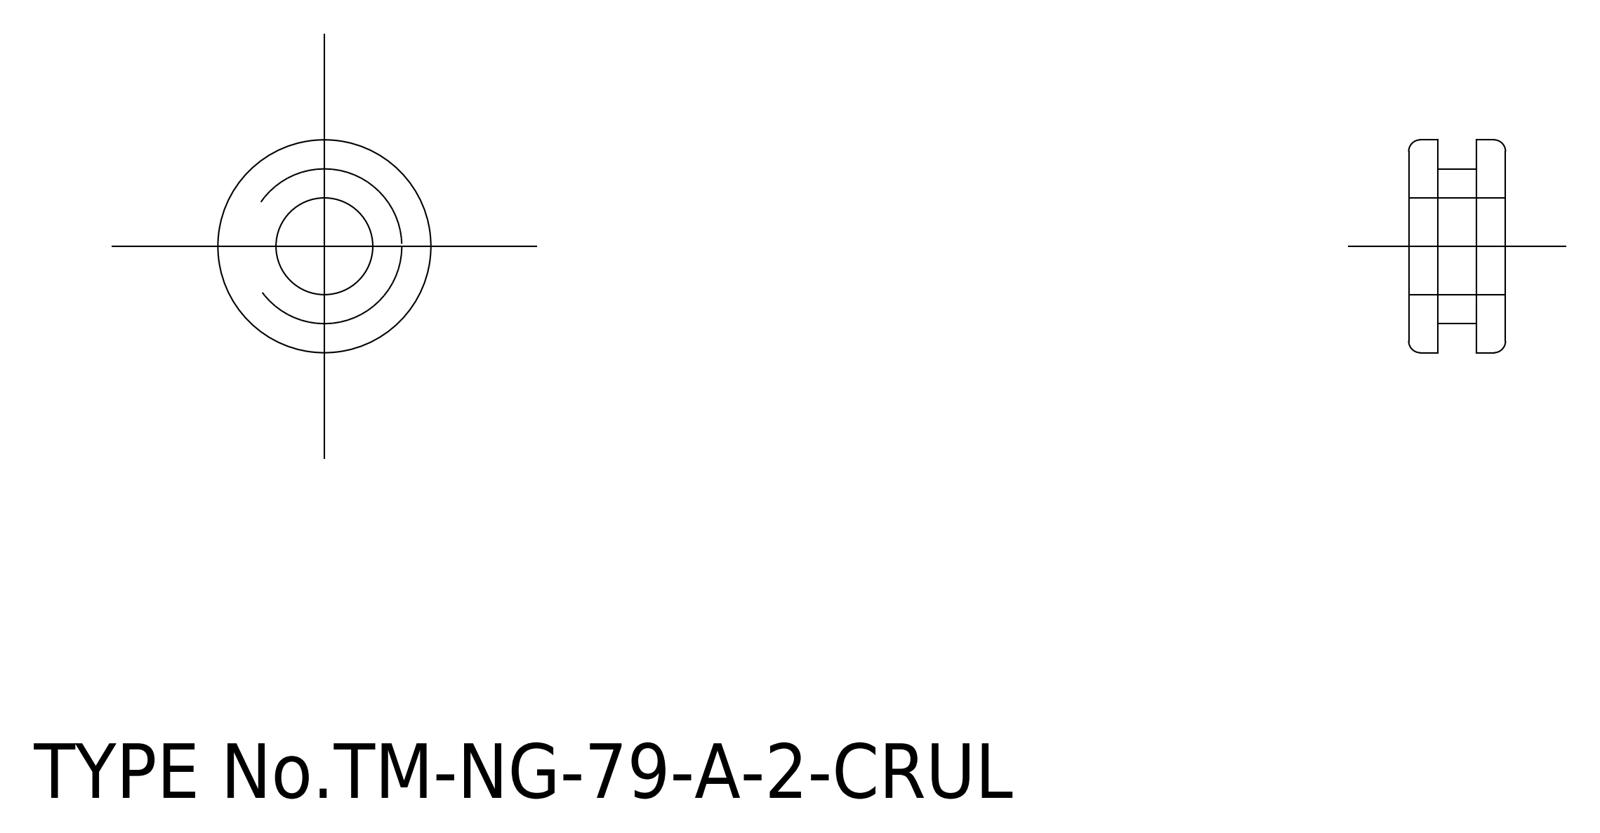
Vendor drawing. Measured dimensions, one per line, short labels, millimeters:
written by: spGate 15.6.1 (AUTOMOTIVE_DESIGN)
unit: mm
bodies: 1 solid, 16 faces (4 planar, 8 cylindrical, 4 other)
size: 11 × 11 × 5
volume: 282 mm³; area: 455 mm²
holes: 1× ⌀5
bosses: 1× ⌀11, 1× ⌀8
face distances: 1.5, 3.5, 5, 2
